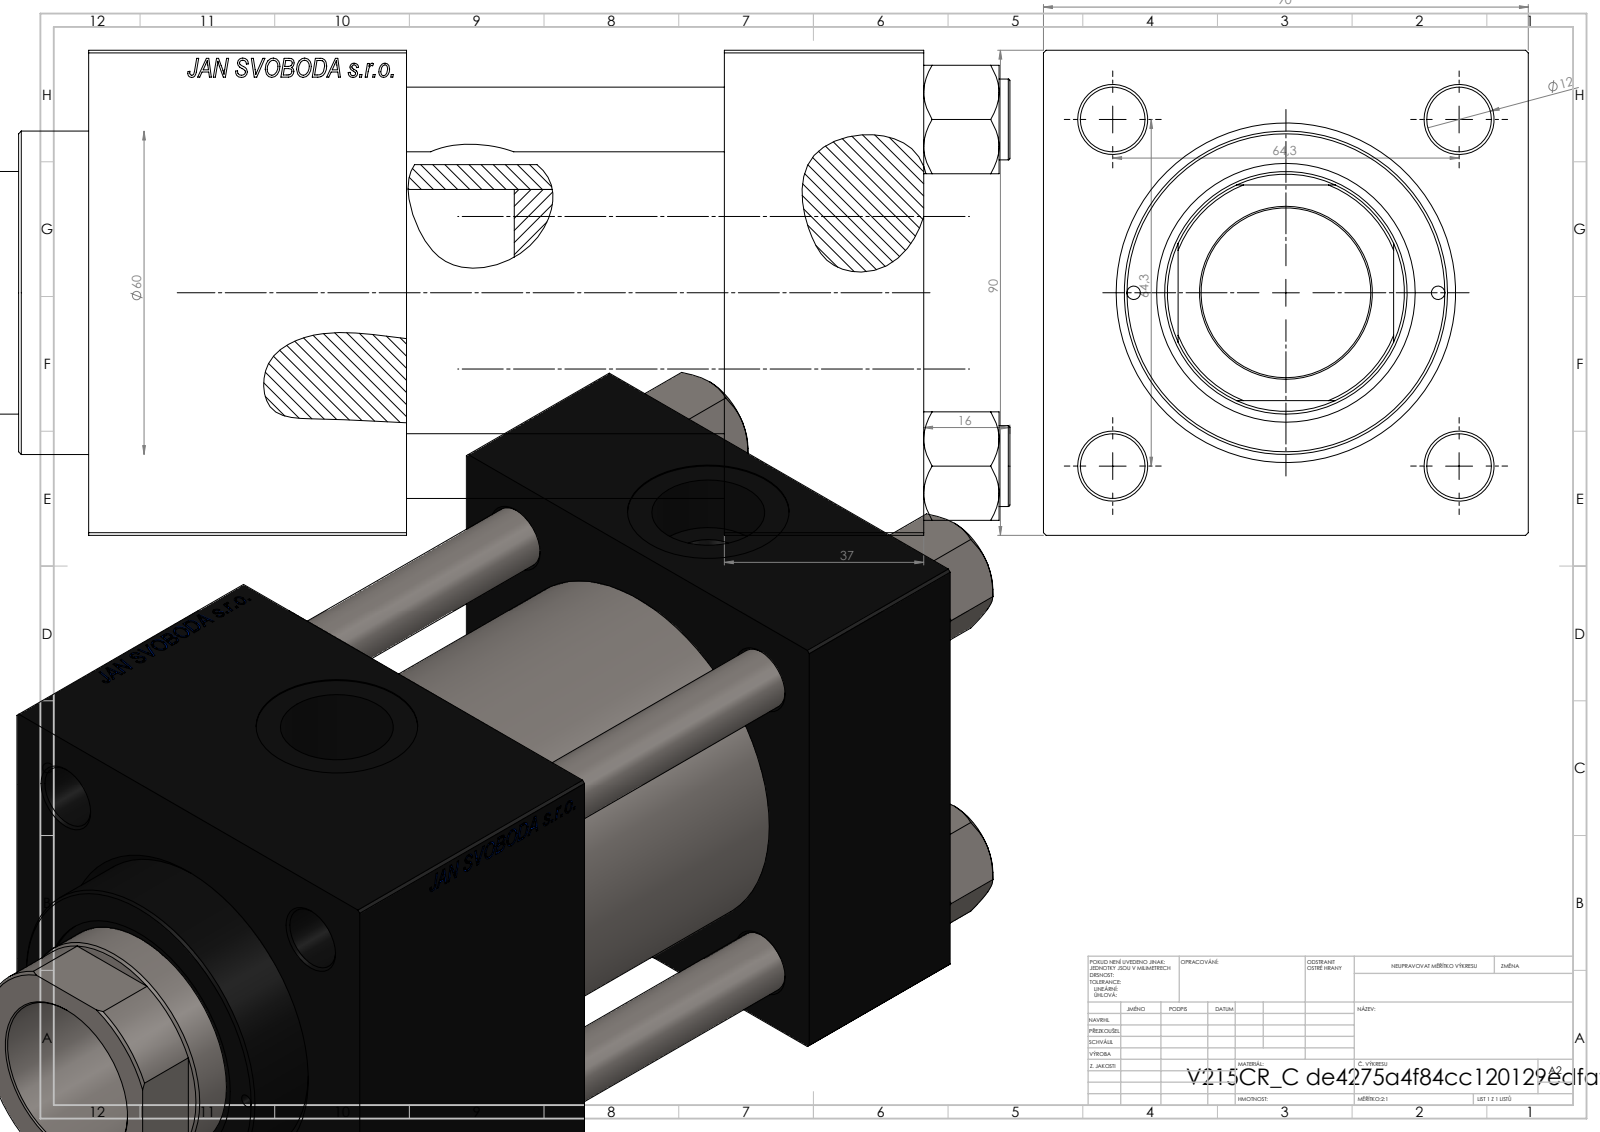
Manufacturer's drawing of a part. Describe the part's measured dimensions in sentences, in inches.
The part is named "V215CR_C_Body; NUT_M5_C; V215CR_VCP_C; V215_VC_A (+1 more)". Its 3-D file was written by "SolidWorks 2019 (CONFIG_CONTROL_DESIGN)". It is 11 solids with 1152 faces: 527 planar, 89 cylindrical and 536 other. Overall it measures 7.992 by 3.543 by 3.543 inches. Its volume is 60.88 cubic inches and its surface area 294.8 square inches. Round holes: 4 of diameter 0.472, 2 of diameter 0.098, 2 of diameter 0.276, 2 of diameter 0.825, 2 of diameter 1.181, 1 of diameter 1.24, 1 of diameter 1.772, 1 of diameter 1.89, 1 of diameter 1.969, 1 of diameter 2.362, 1 of diameter 2.48. Round bosses or shafts: 4 of diameter 0.591, 1 of diameter 2.717. Partial cylindrical surfaces (rounded edges, fillets, slot ends): 1 of radius 0.866. The main face-to-face distances are 3.543, 2.323, 1.457, 3.78, 6.102, 4.646, 4.972, 3.516, 1.193, 1.13. The hole center spacings are 1.275, 1.79, 2.531, 2.694, 1.112, 3.58, 2.224, 3.839.
